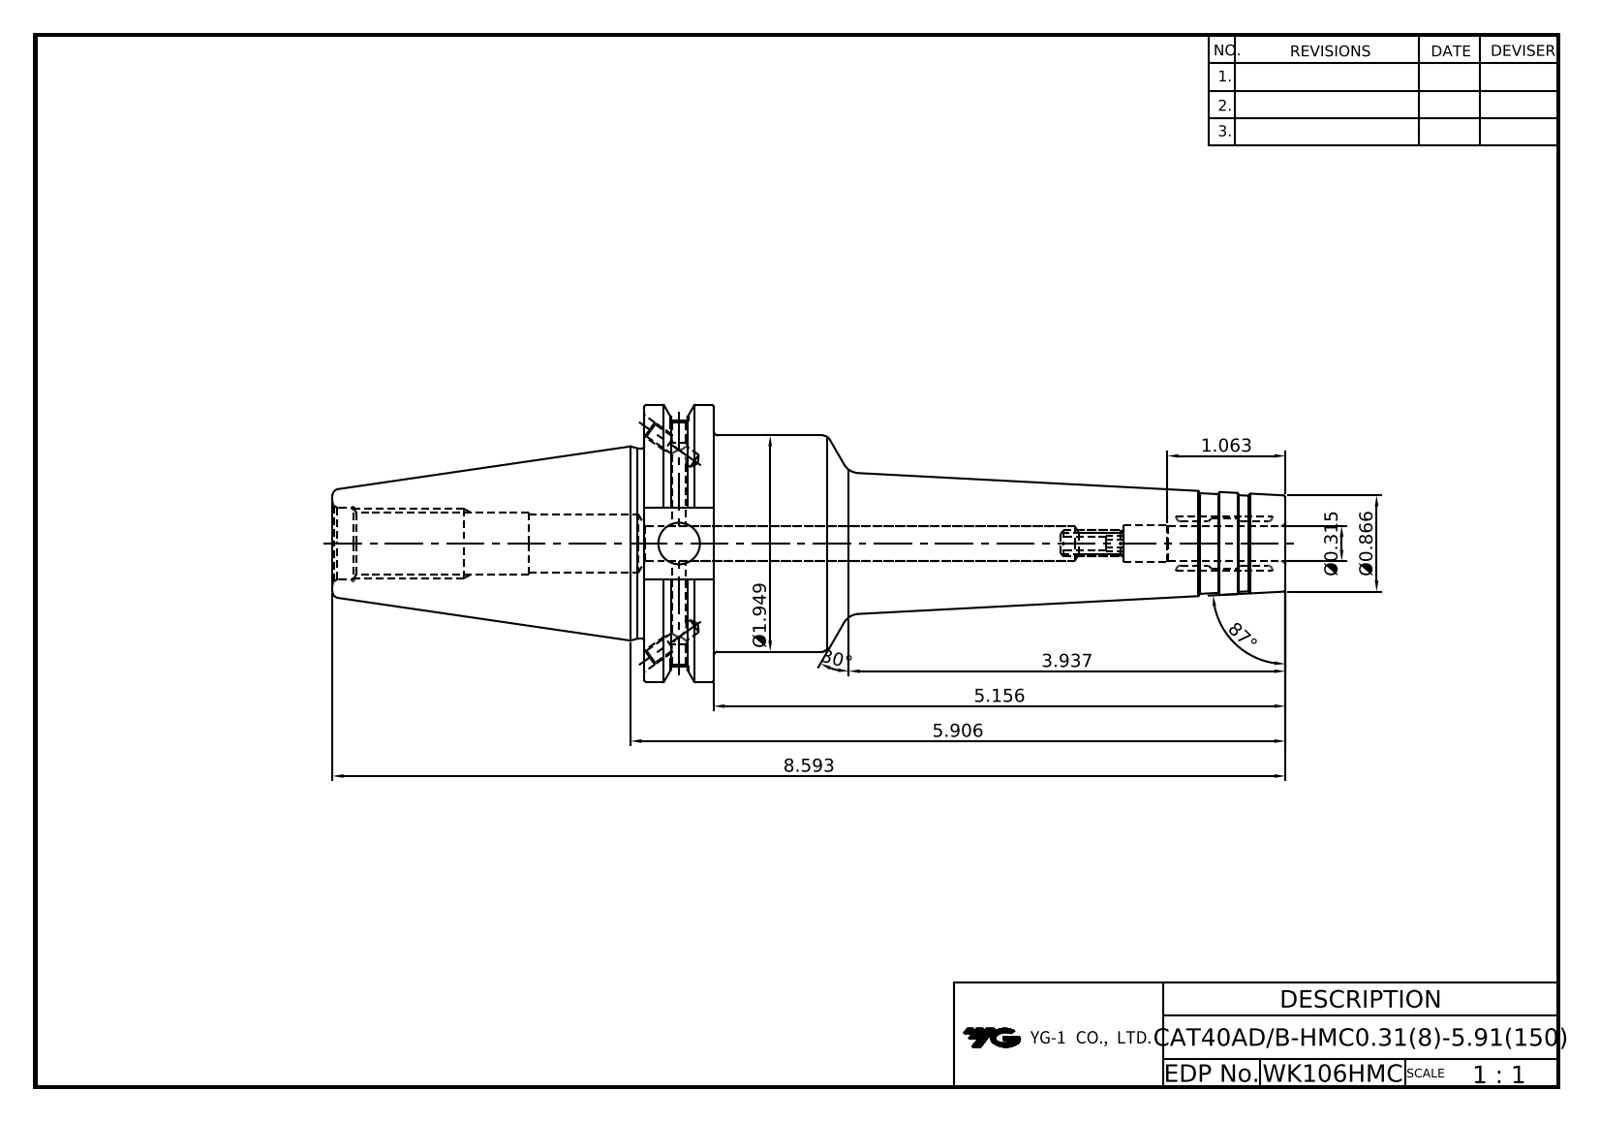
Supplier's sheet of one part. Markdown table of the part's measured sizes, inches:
| quantity | value |
| --- | --- |
| part name | WK106HMC-CAT40ADB-HMC0_31-5_91 |
| STEP written by | PRO/ENGINEER BY PARAMETRIC TECHNOLOGY CORPORATION, 2012130 (CONFIG_CONTROL_DESIGN) |
| units | inches |
| bodies | 1 solid, 187 faces (35 planar, 67 cylindrical, 85 other) |
| overall size | 8.593 × 2.5 × 2.416 |
| volume | 12.87 in³ |
| surface area | 57.8 in² |
| round holes (diameter × count) | 0.13 × 3, 0.138 × 3, 0.157 × 3, 0.165 × 2, 0.215 × 1, 0.315 × 1, 0.331 × 1, 0.375 × 1, 0.531 × 1, 0.551 × 1, 0.642 × 1 |
| round bosses / shafts (diameter × count) | 2.5 × 1, 1.948 × 1, 1.717 × 1 |
| partial cylindrical surfaces (radius × count) | 0.322 × 1, 1.108 × 1 |
| main face-to-face distances | 0.625, 5.781, 5.156, 1.898, 0.644, 0.239, 0.386, 5.542, 0.389, 0.15 |
